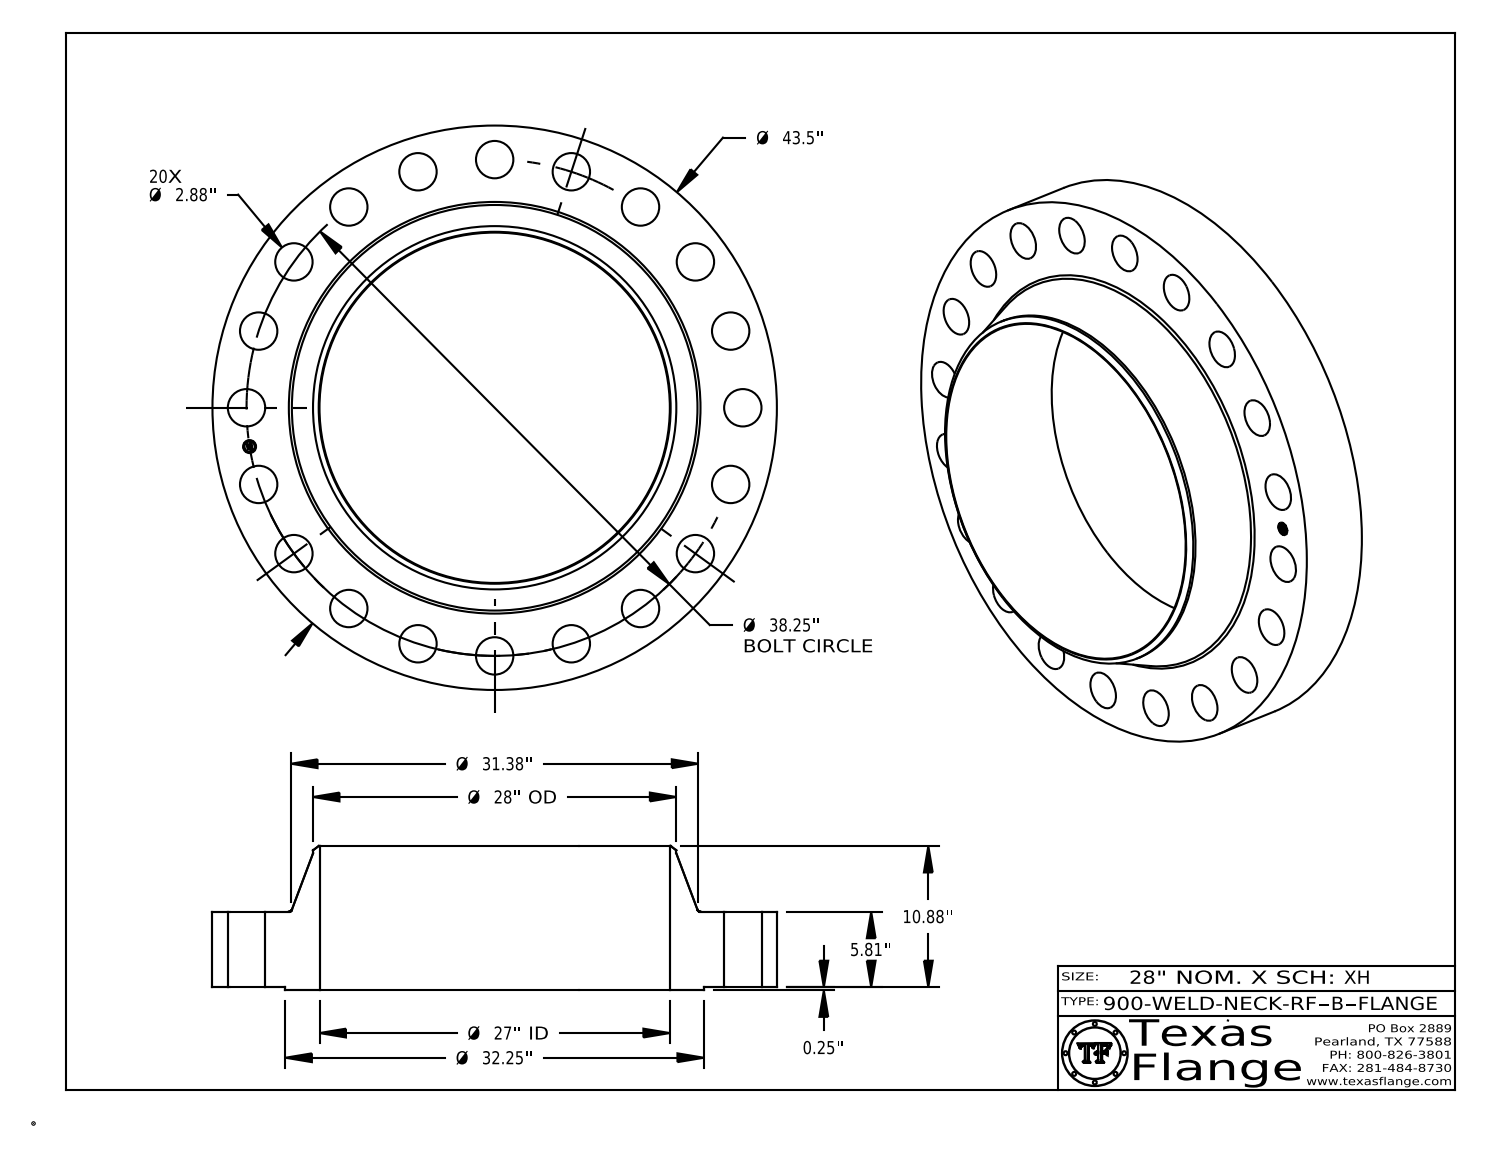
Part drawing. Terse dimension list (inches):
name: 900-WELD-NECK-RF, Series B
written by: CATIA V5 STEP AP214 (AUTOMOTIVE_DESIGN)
unit: in
bodies: 1 solid, 443 faces (369 planar, 68 cylindrical, 6 other)
size: 43.5 × 43.5 × 11.13
volume: 5 173 in³; area: 4 699 in²
holes: 20× ⌀2.88, 1× ⌀1, 1× ⌀27
bosses: 8× ⌀0.061, 1× ⌀43.5, 1× ⌀32.25, 1× ⌀28, 1× ⌀0.788
face distances: 5.81, 0.25, 6.06, 11.13, 10.88, 5.07, 6.045, 5.795, 0.015, 5.085
hole spacings: 30.945, 36.378, 37.779, 19.125, 11.82, 27.047, 34.081, 5.984
